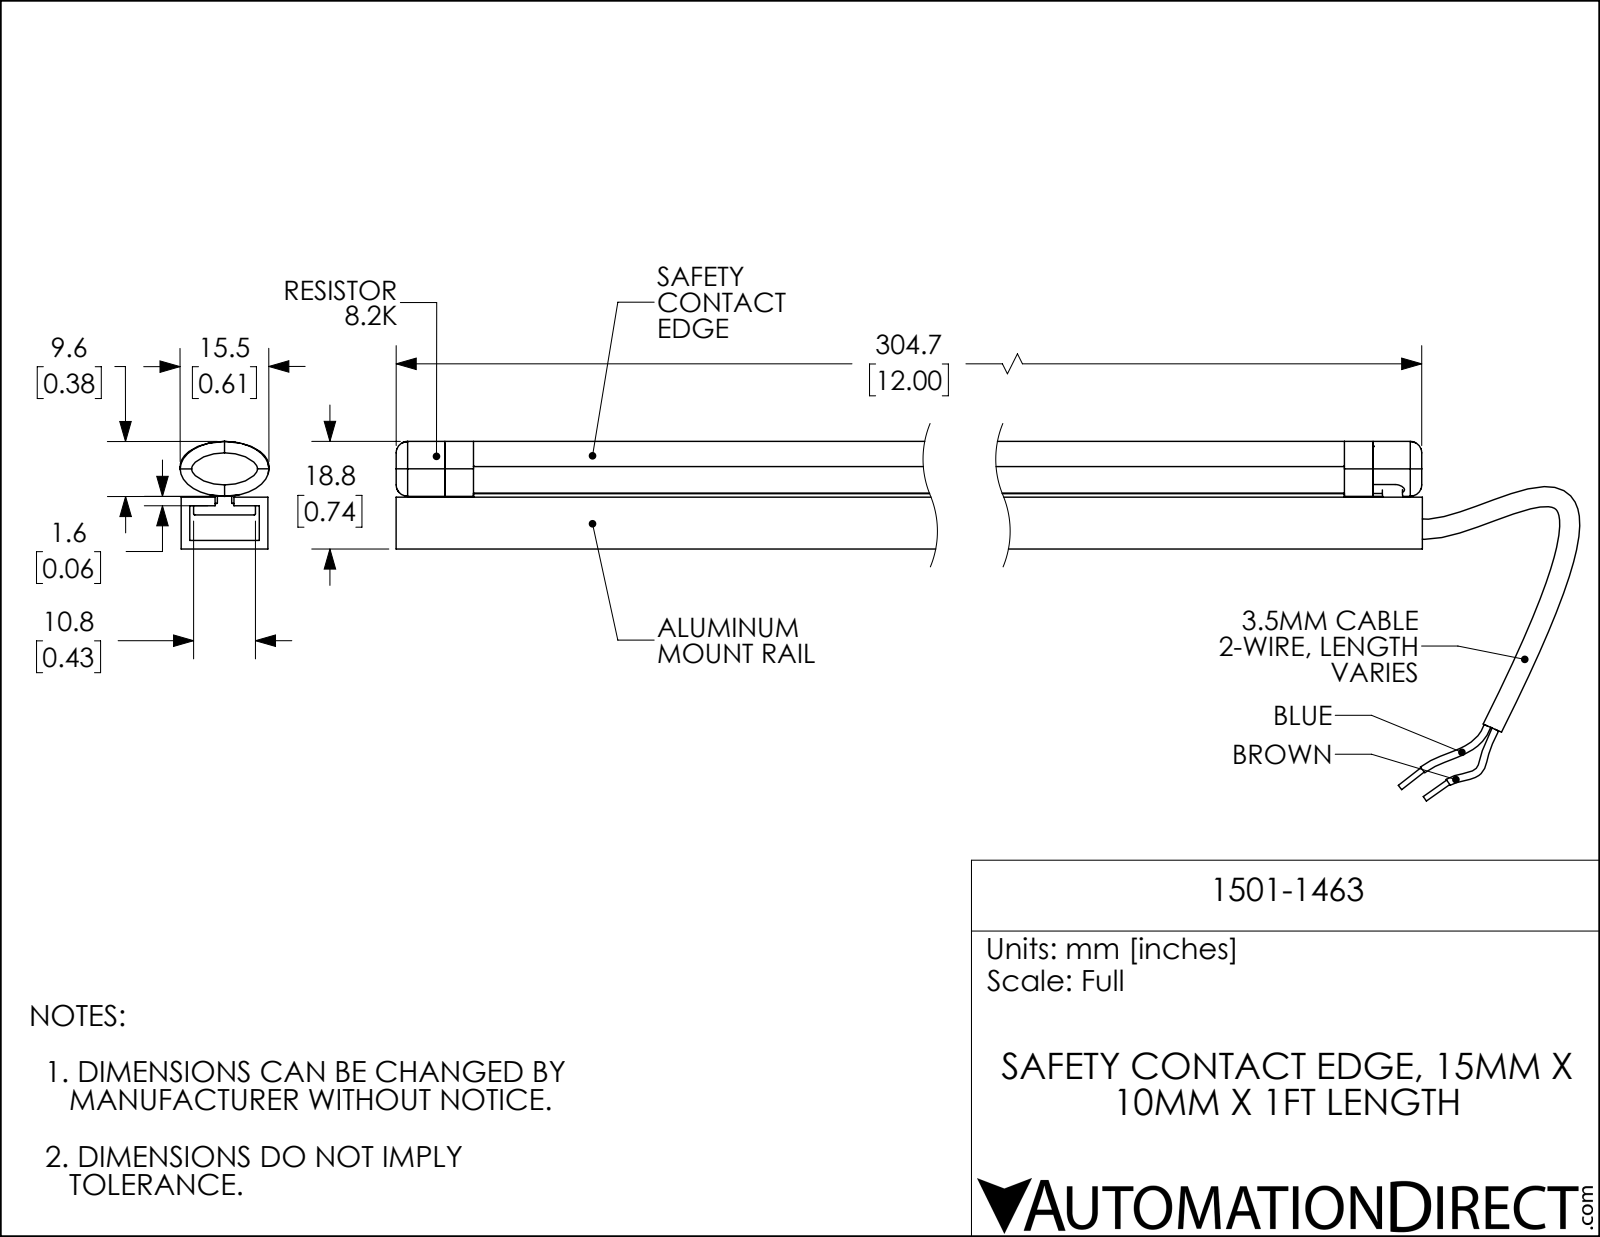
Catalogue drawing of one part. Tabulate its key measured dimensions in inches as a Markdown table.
| quantity | value |
| --- | --- |
| part name | 1501-1463 |
| STEP written by | SolidWorks 2018 (AUTOMOTIVE_DESIGN) |
| units | inches |
| bodies | 7 solids, 607 faces (129 planar, 154 cylindrical, 324 other) |
| overall size | 13.082 × 2.471 × 0.611 |
| volume | 3.007 in³ |
| surface area | 86.73 in² |
| round holes (diameter × count) | 0.047 × 4 |
| round bosses / shafts (diameter × count) | 0.037 × 2 |
| partial cylindrical surfaces (radius × count) | 0.004 × 52, 0.016 × 15, 0.012 × 10, 0.008 × 7, 0.02 × 4, 0.512 × 4, 0.008 × 3, 0.059 × 3 |
| main face-to-face distances | 0.059, 0.297, 0.537, 0.356, 0.016, 0.122, 0.234, 0.175, 0.596, 0.238 |
| hole center spacings | 0.197, 0.196, 0.197 |
